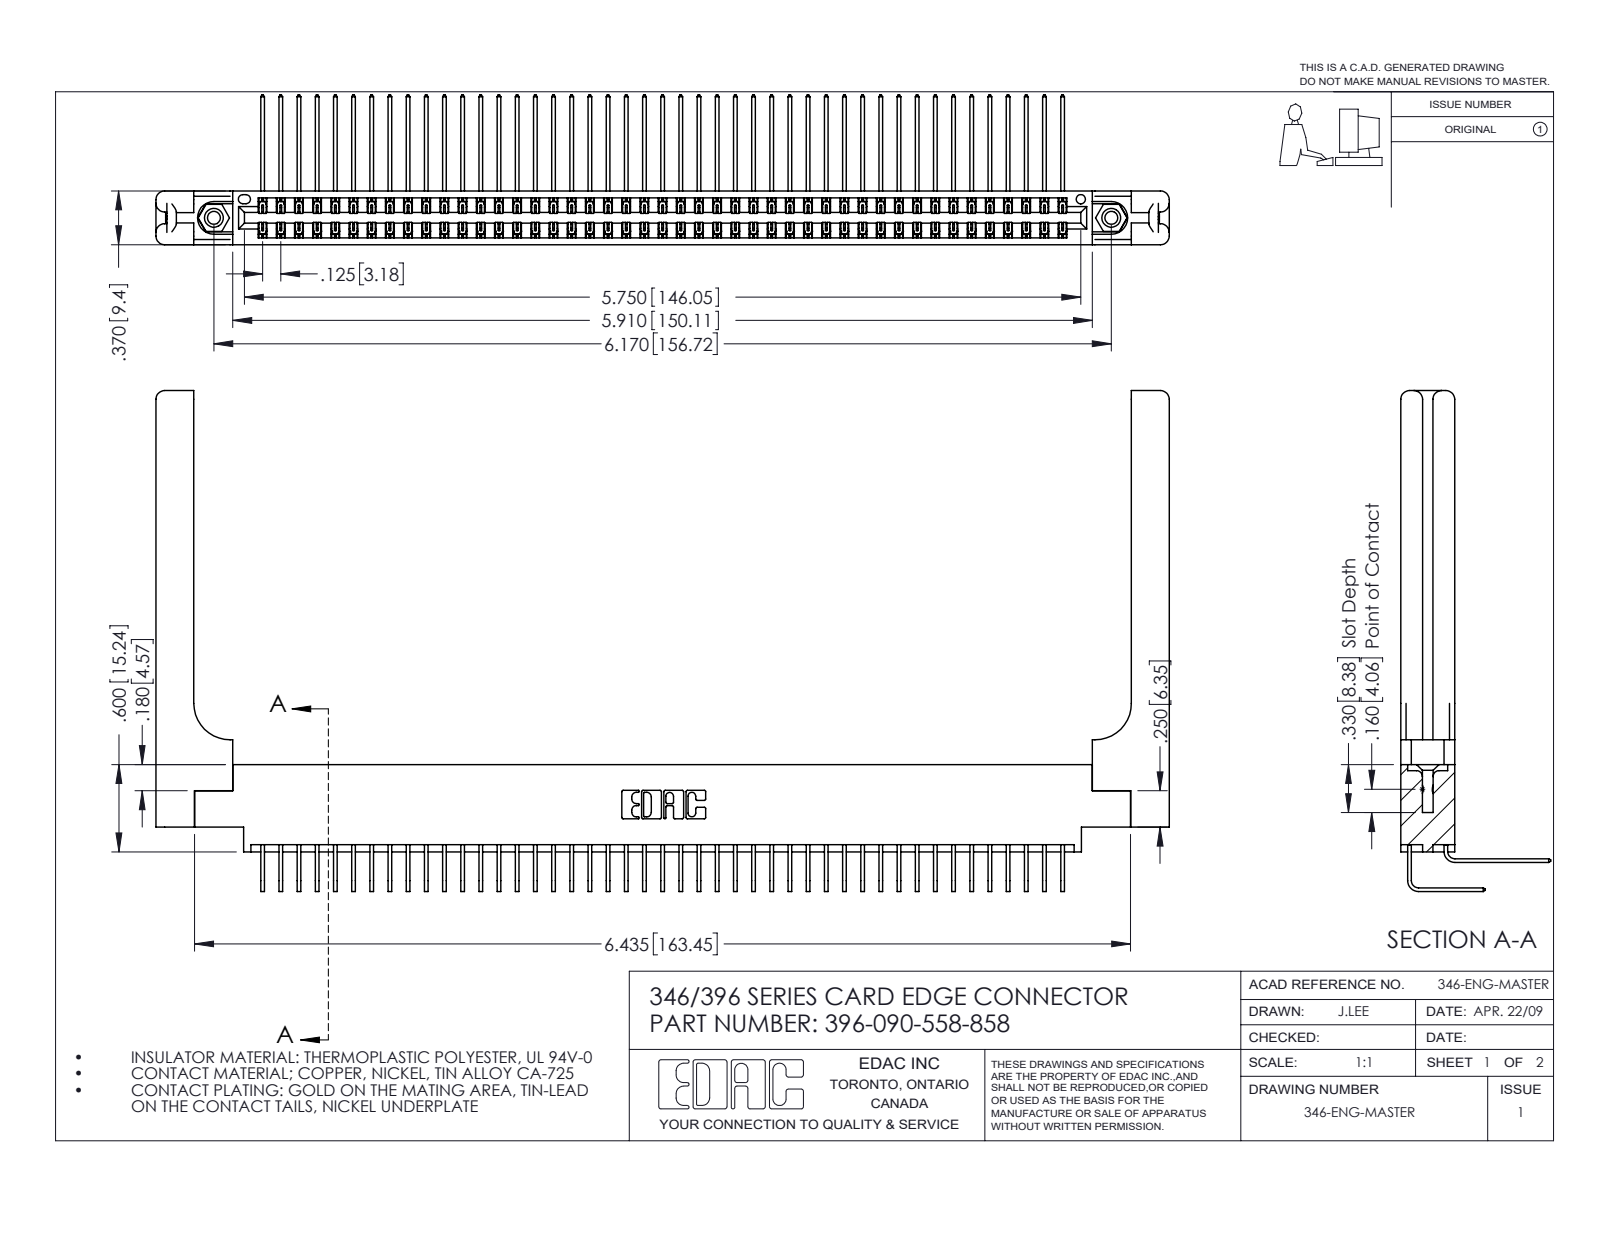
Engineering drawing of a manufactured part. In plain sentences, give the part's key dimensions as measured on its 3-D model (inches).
The part is named "345-292-001_558 Tail - 2; 345-292-001_558 559 Tail - 1; 346 Part_0.170 Offset - 0.156 Dia-TH; 396-090-558-858 (+2 more)". Its 3-D file was written by "SolidWorks 2016 (CONFIG_CONTROL_DESIGN)". It is 95 solids with 5242 faces: 3558 planar, 1624 cylindrical and 60 other. Overall it measures 6.966 by 3.443 by 1.03 inches. Its volume is 1.534 cubic inches and its surface area 49.51 square inches. Round holes: 2 of diameter 0.089, 2 of diameter 0.125, 2 of diameter 0.156, 1 of diameter 0.064. Round bosses or shafts: 2 of diameter 0.155. Partial cylindrical surfaces (rounded edges, fillets, slot ends): 135 of radius 0.006, 22 of radius 0.01, 16 of radius 0.06, 6 of radius 0.007, 6 of radius 0.031, 3 of radius 0.026, 2 of radius 0.014, 2 of radius 0.022. The main face-to-face distances are 0.322, 0.048, 0.37, 0.072, 0.025, 0.298, 0.148, 0.15, 0.25, 0.275. The hole center spacings are 0.246, 5.961, 6.17.
